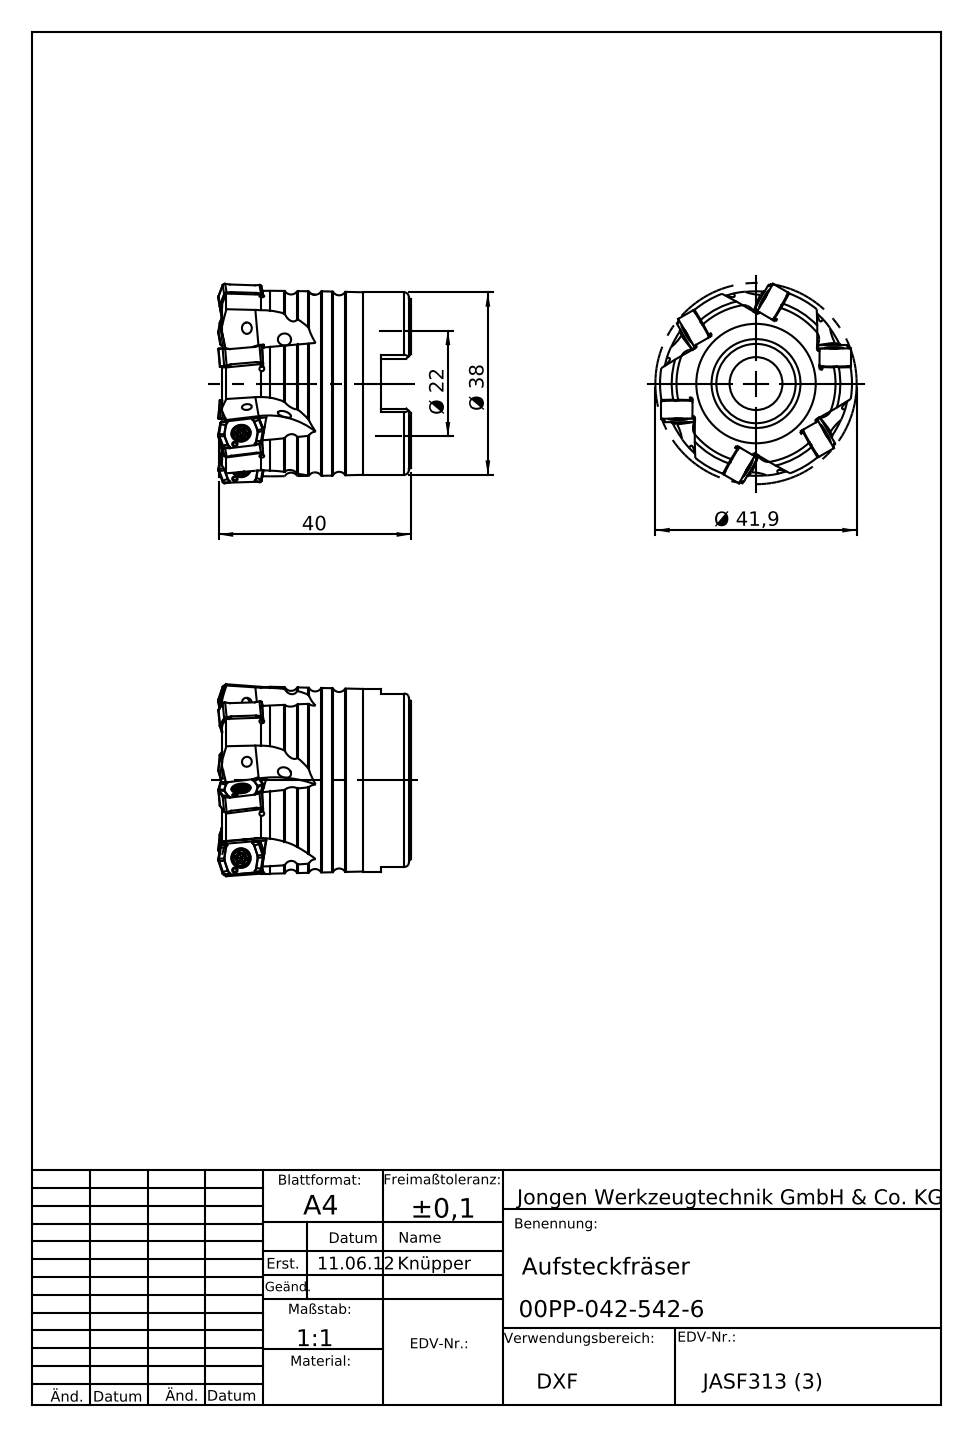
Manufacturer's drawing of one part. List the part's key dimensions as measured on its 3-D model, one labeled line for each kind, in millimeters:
Part name (STEP PRODUCT): 00PP-042-542-6
STEP written by: SolidWorks 2013 (AUTOMOTIVE_DESIGN)
Units: millimetres
Bodies: 1 solid, 207 faces (96 planar, 24 cylindrical, 87 other)
Overall size (bounding box): 38.9 × 38.62 × 38.55
Volume: 26 093 mm³ · Surface area: 9 276 mm²
Round holes (diameter × count): ⌀2.5 ×6, ⌀11 ×1, ⌀16.5 ×1, ⌀22 ×1, ⌀22.15 ×1, ⌀22.3 ×1
Round bosses / shafts (diameter × count): ⌀38 ×1
Partial cylindrical surfaces — rounded edges, fillets, slot ends (radius × count): R15 ×6, R19.45 ×1
Main face-to-face distances: 37.8, 6.3, 31.5, 19.95, 13.65, 17.85, 26.8, 20.5, 6.85, 11
